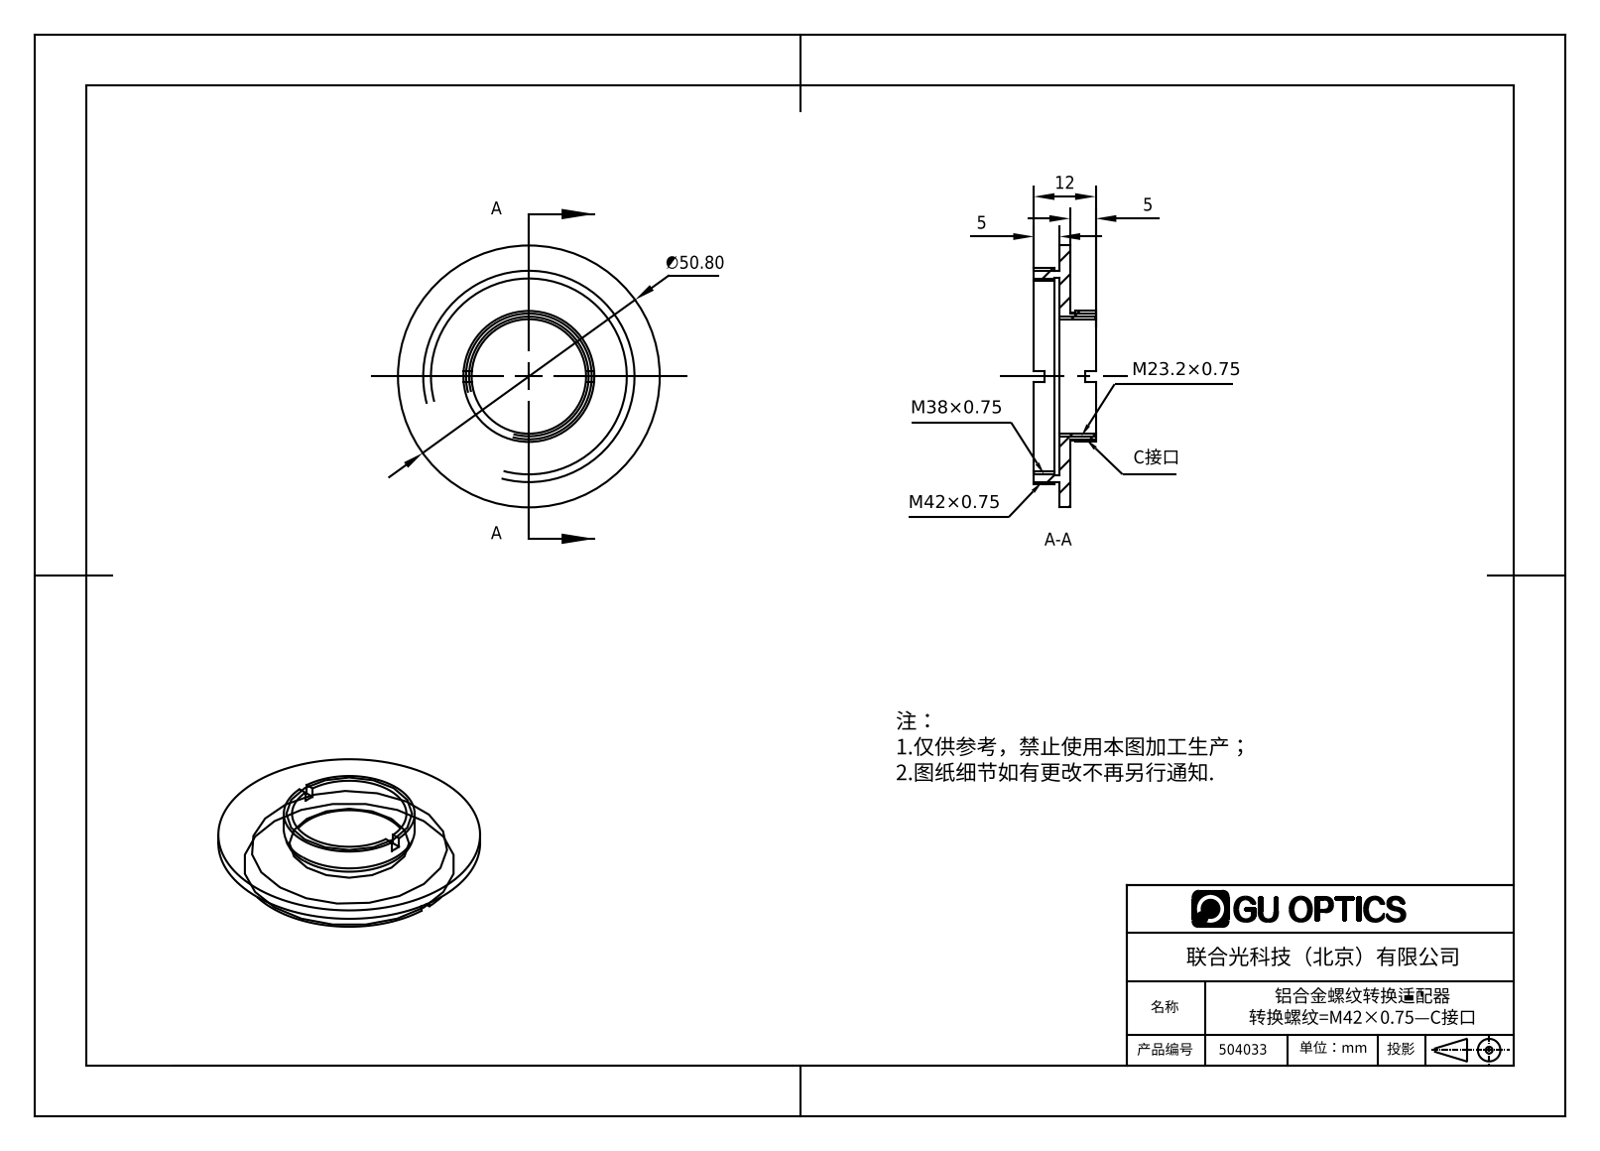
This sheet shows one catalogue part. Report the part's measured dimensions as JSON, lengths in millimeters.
{"part_name": "504033", "step_written_by": "SolidWorks 2016 (AUTOMOTIVE_DESIGN)", "units": "millimeters", "bodies": {"solids": 1, "faces": 38, "planar": 22, "cylindrical": 16, "other": 0}, "overall_size": [50.8, 50.8, 12], "volume_mm3": 5236, "surface_area_mm2": 6046, "round_holes": [[22.2, 1], [37, 1], [38.2, 1]], "round_bosses_or_shafts": [[50.8, 1], [42, 1], [41, 1], [25.4, 1], [24.8, 1]], "face_to_face_distances": [2, 5, 7, 4, 3, 1, 8, 12, 10, 6]}
